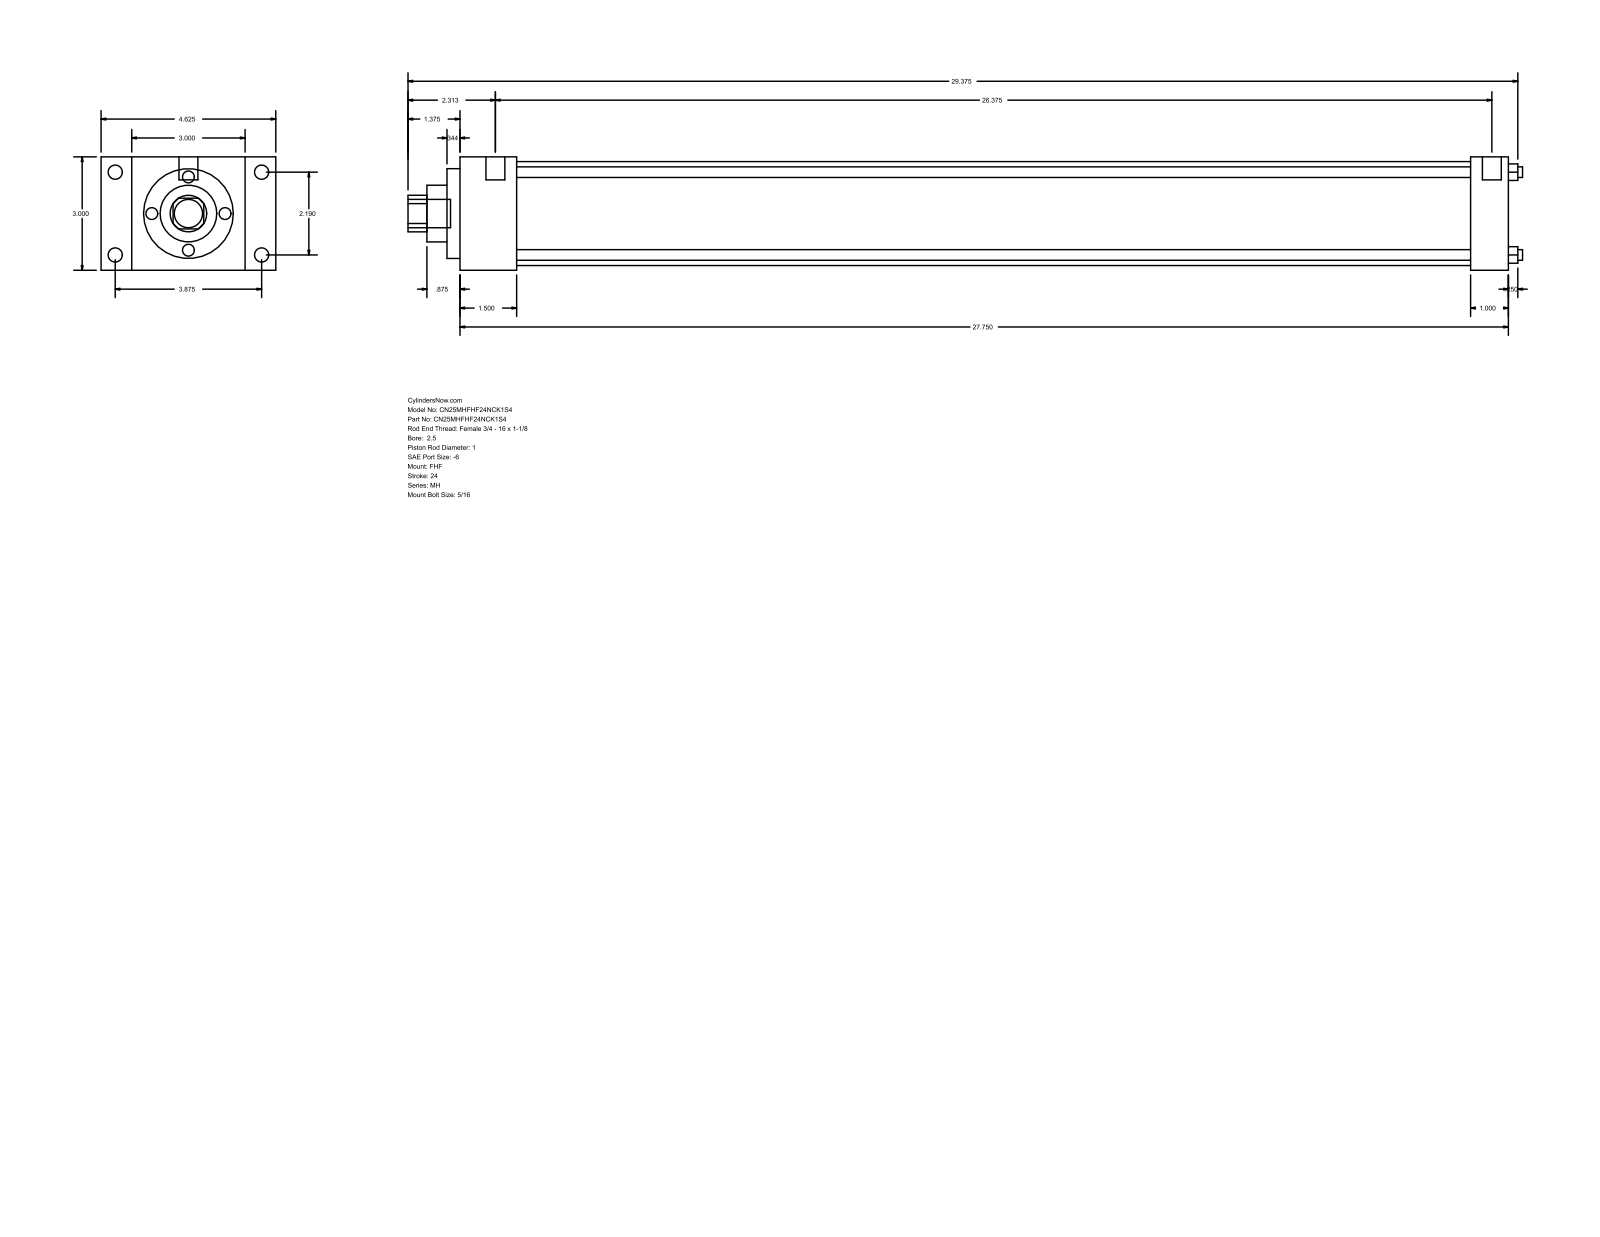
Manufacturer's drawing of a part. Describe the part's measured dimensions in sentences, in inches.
The part is named "MH_FHF__0250_1". Its 3-D file was written by "GSSL Pune (CONFIG_CONTROL_DESIGN)". It is 0 solids with 90 faces: 61 planar, 29 cylindrical and 0 other. Overall it measures 29.5 by 4.625 by 3 inches. Round holes: 4 of diameter 0.281, 1 of diameter 1, 1 of diameter 1.5, 1 of diameter 2.375, 1 of diameter 2.75. Round bosses or shafts: 4 of diameter 0.375, 4 of diameter 0.219, 2 of diameter 0.5, 1 of diameter 0.75. Partial cylindrical surfaces (rounded edges, fillets, slot ends): 1 of radius 0.484. The main face-to-face distances are 3, 27.75, 1.5, 26.25, 0.813, 3.813, 4.625, 1, 26.75, 25.25. The hole center spacings are 1.548, 2.19, 3.097.
